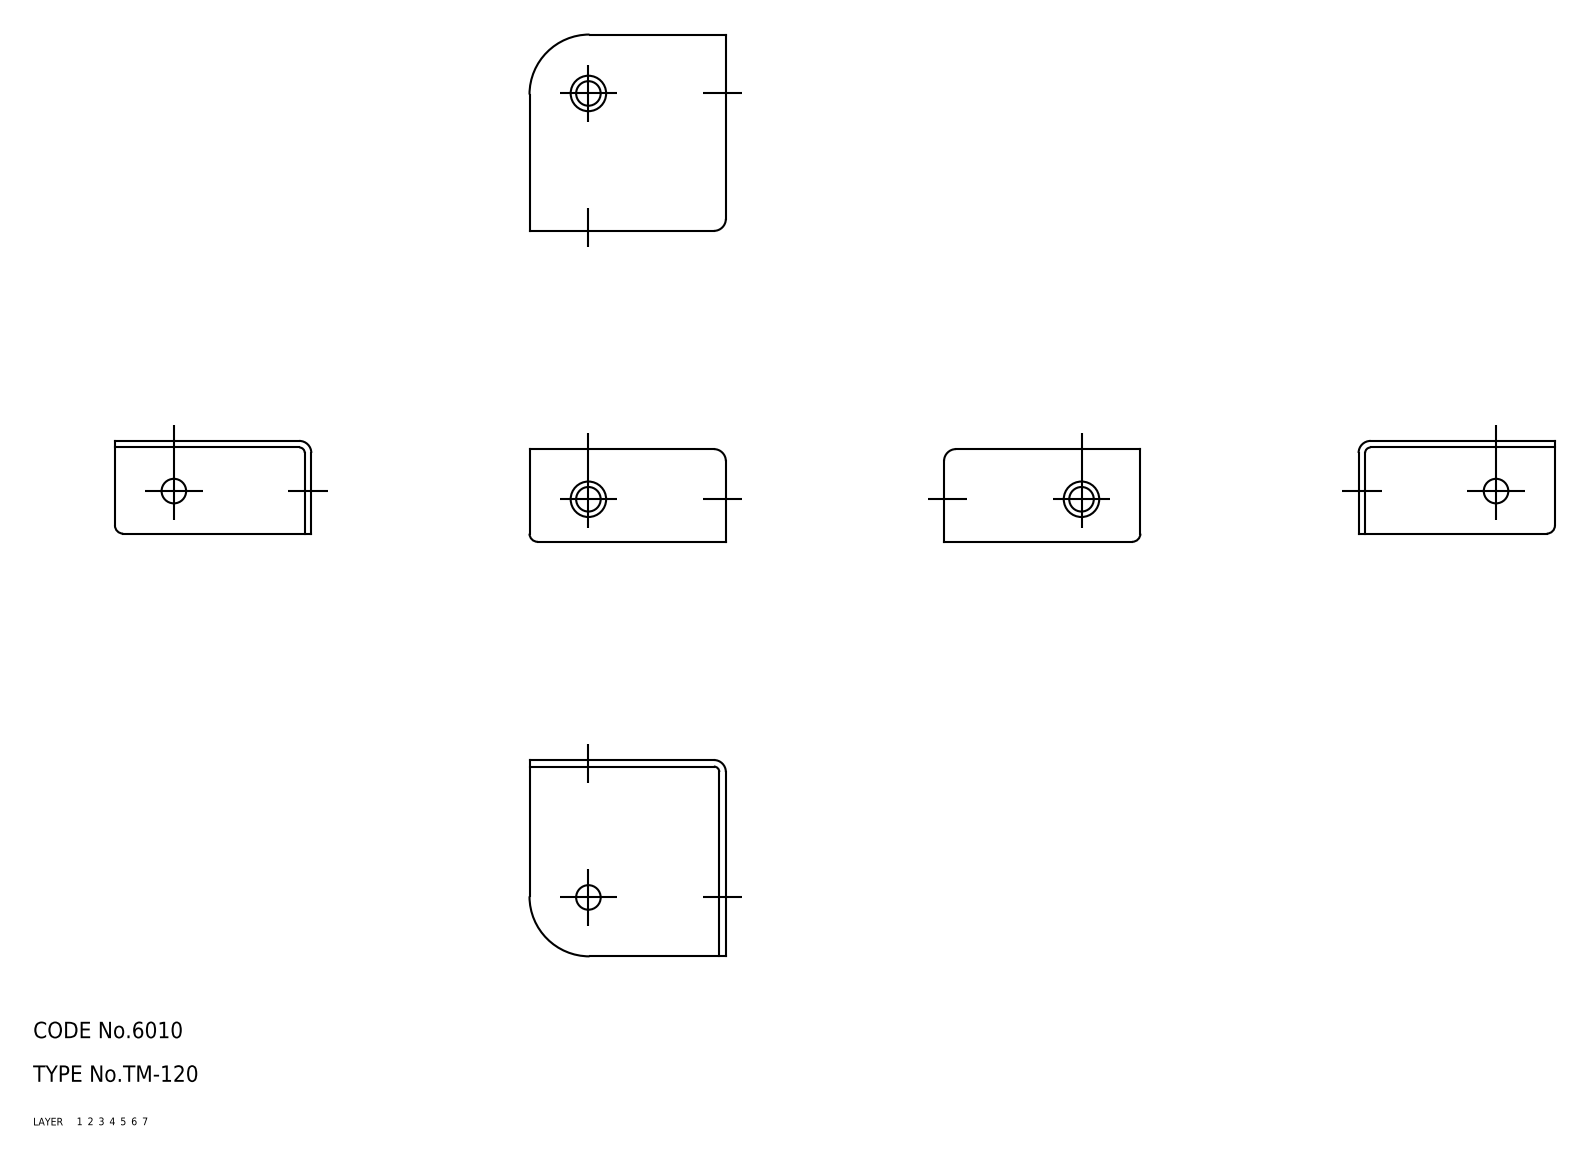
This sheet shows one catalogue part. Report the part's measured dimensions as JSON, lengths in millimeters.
{"part_name": "angle", "step_written_by": "CADfix (AUTOMOTIVE_DESIGN)", "units": "millimeters", "bodies": {"solids": 1, "faces": 32, "planar": 0, "cylindrical": 0, "other": 32}, "overall_size": [36, 36, 17], "volume_mm3": 2711, "surface_area_mm2": 4790}
